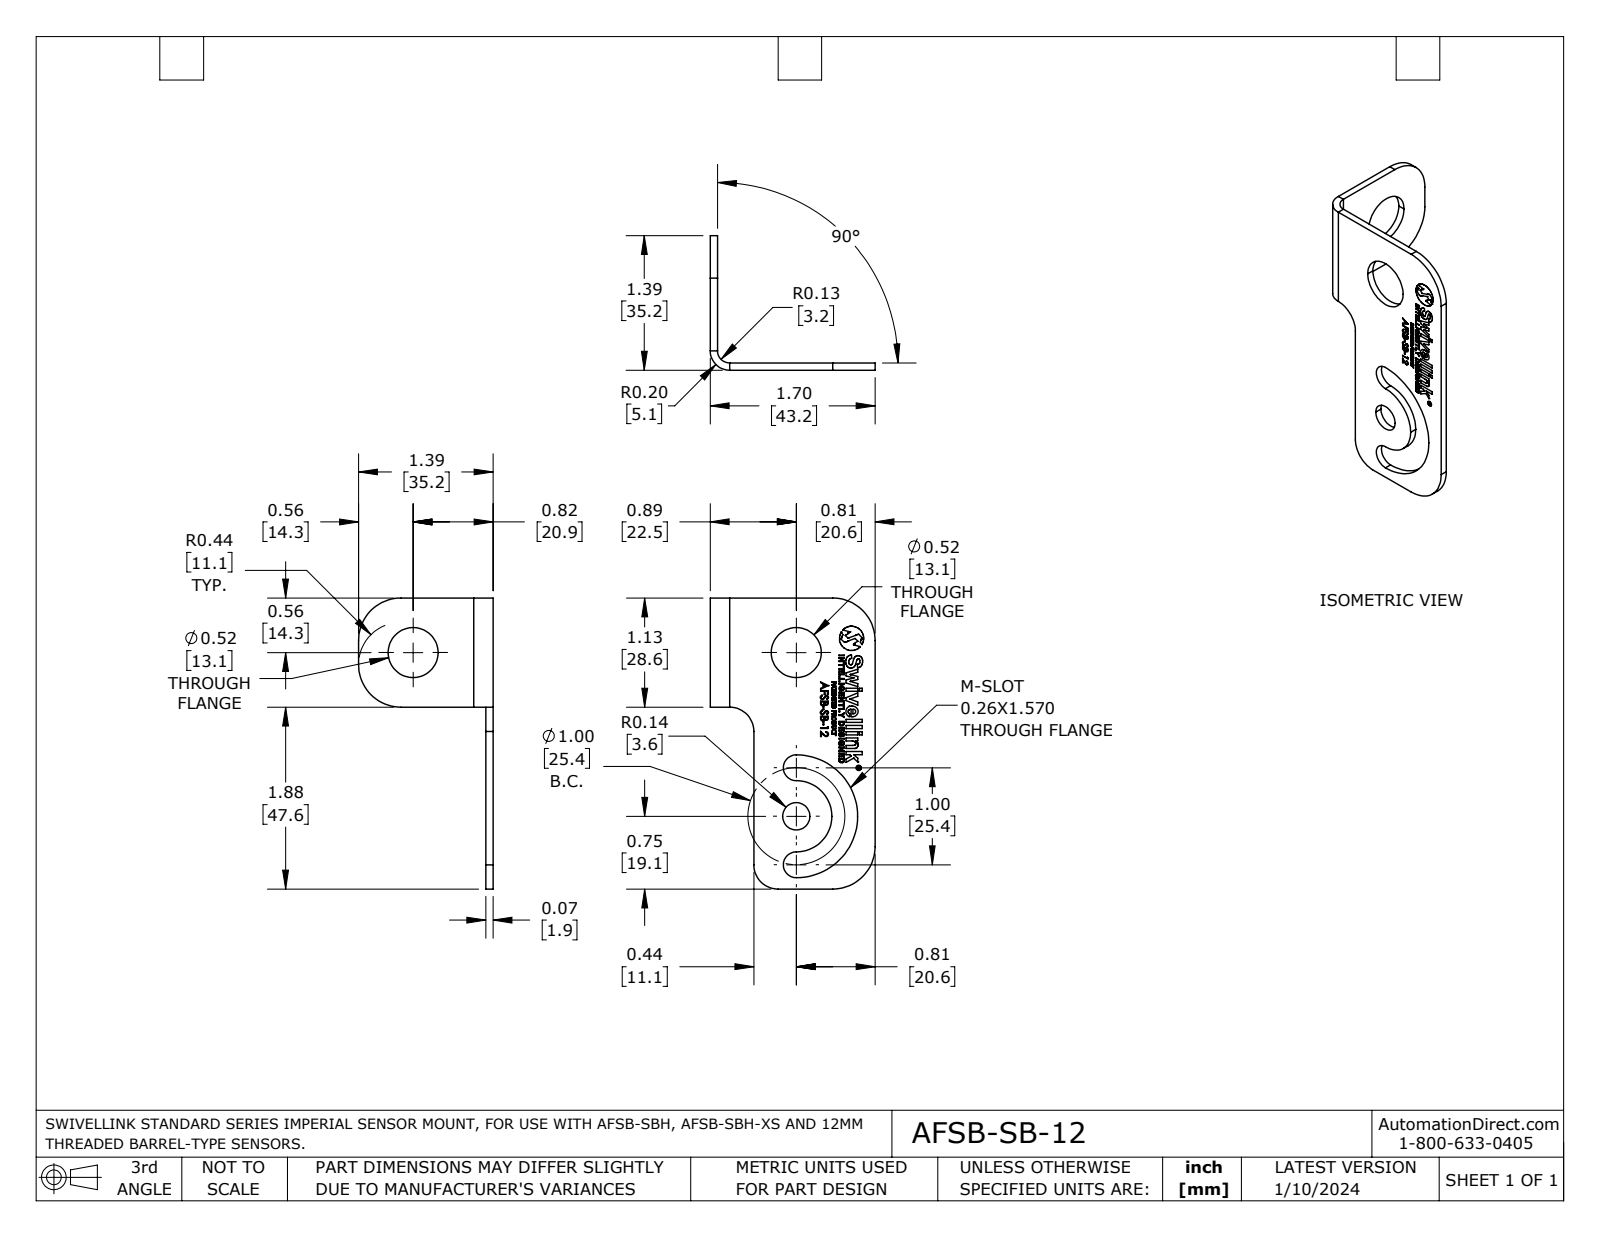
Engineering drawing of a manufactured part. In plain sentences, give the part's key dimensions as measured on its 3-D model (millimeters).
The part is named "AFSB-SB-12". Its 3-D file was written by "SolidWorks 2023 (AUTOMOTIVE_DESIGN)". It is 1 solid with 111 faces: 91 planar, 20 cylindrical and 0 other. Overall it measures 76.2 by 43.2 by 35.2 millimeters. Its volume is 5 560 cubic millimeters and its surface area 6 768 square millimeters. Round holes: 2 of diameter 13.1, 1 of diameter 7.1. Partial cylindrical surfaces (rounded edges, fillets, slot ends): 4 of radius 11.1, 2 of radius 3.4, 2 of radius 6.4, 1 of radius 3.2, 1 of radius 5.1, 1 of radius 9.3, 1 of radius 16.1. The main face-to-face distances are 1.9, 41.3, 43.2, 31.8, 9.5, 11.4, 28.6, 76.2, 47.6, 33.3. The hole center spacings are 42.8.
